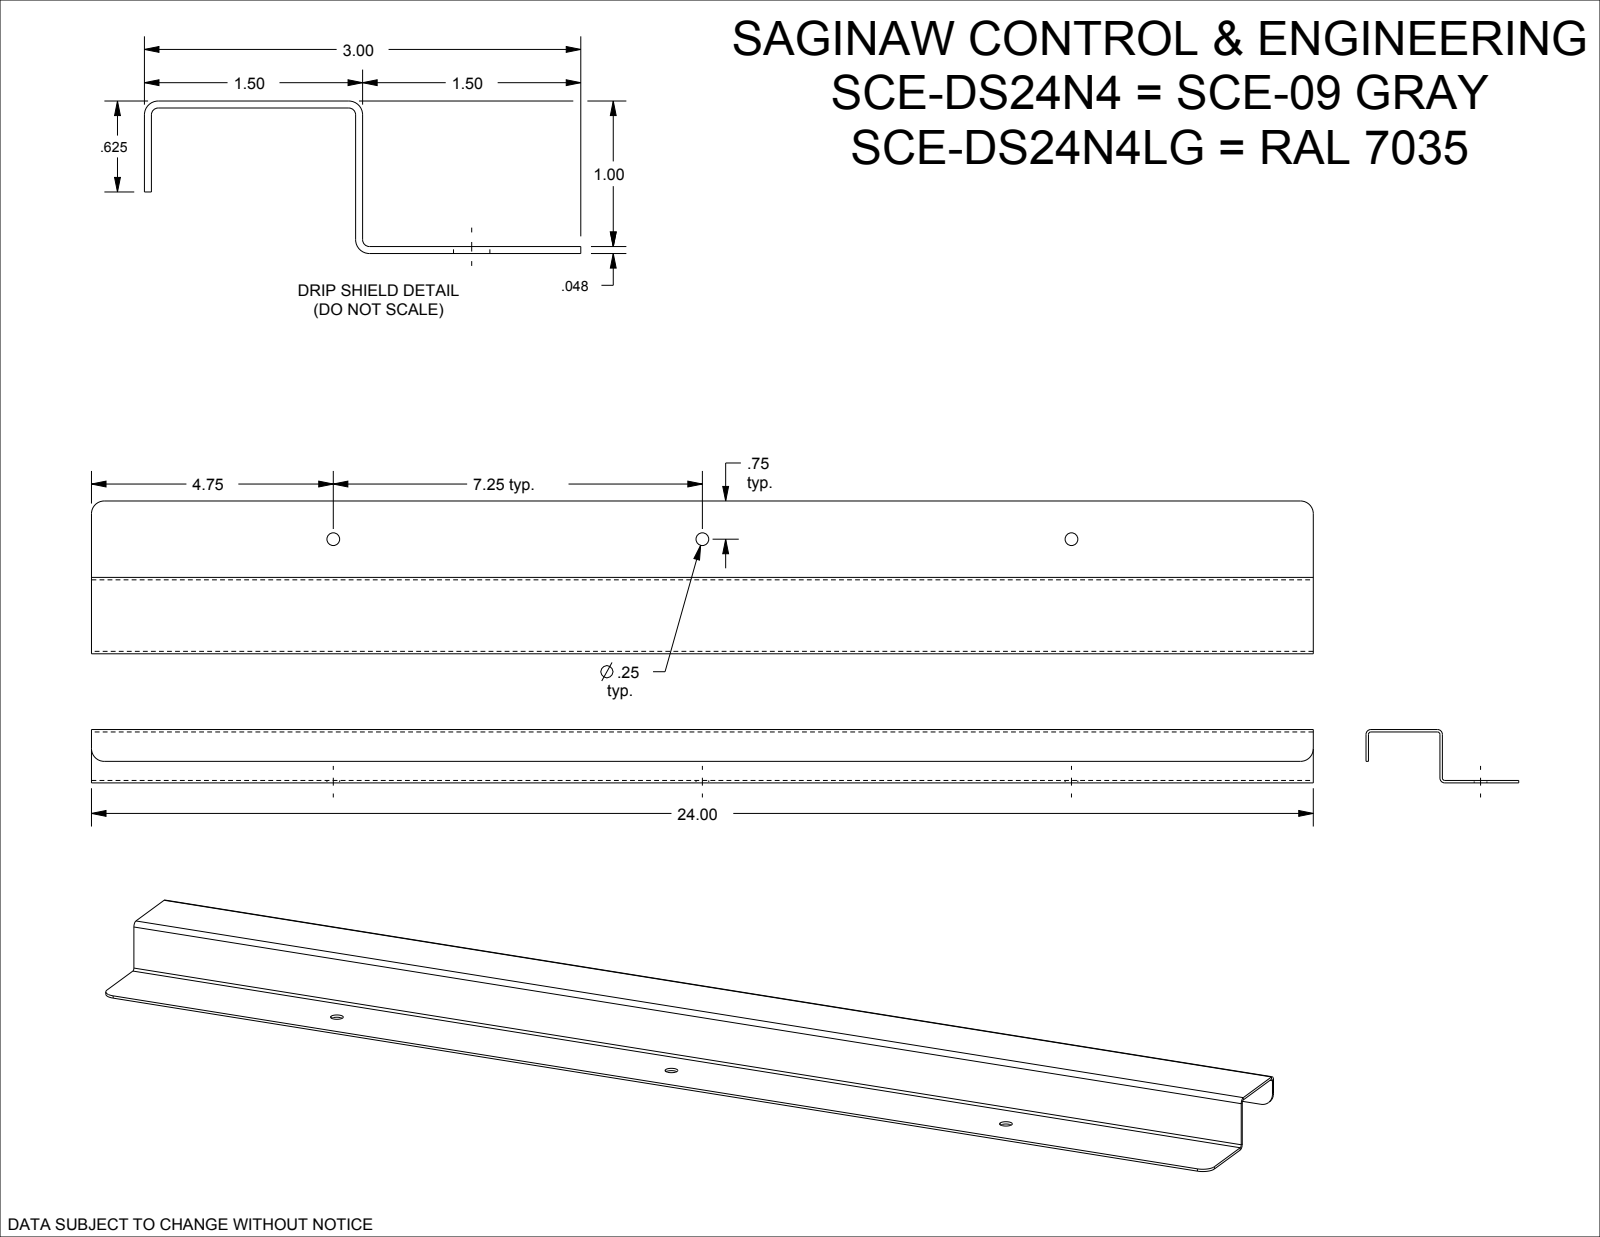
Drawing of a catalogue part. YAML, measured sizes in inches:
part_name: "SCE-DS24N4LG"
step_written_by: "SolidWorks 2019 (CONFIG_CONTROL_DESIGN)"
units: inches
bodies: {solids: 1, faces: 25, planar: 12, cylindrical: 13, other: 0}
overall_size: [24, 3, 1.048]
volume: 5.158
surface_area: 217.7
round_holes:
  - {diameter: 0.25, count: 3}
partial_cylinders:
  - {radius: 0.25, count: 4}
  - {radius: 0.047, count: 3}
  - {radius: 0.095, count: 3}
face_to_face_distances: [0.048, 1, 1.048, 0.952, 1.452, 1.5, 1.404, 0.423, 0.375, 0.577]
hole_center_spacings: [7.25, 14.5]
